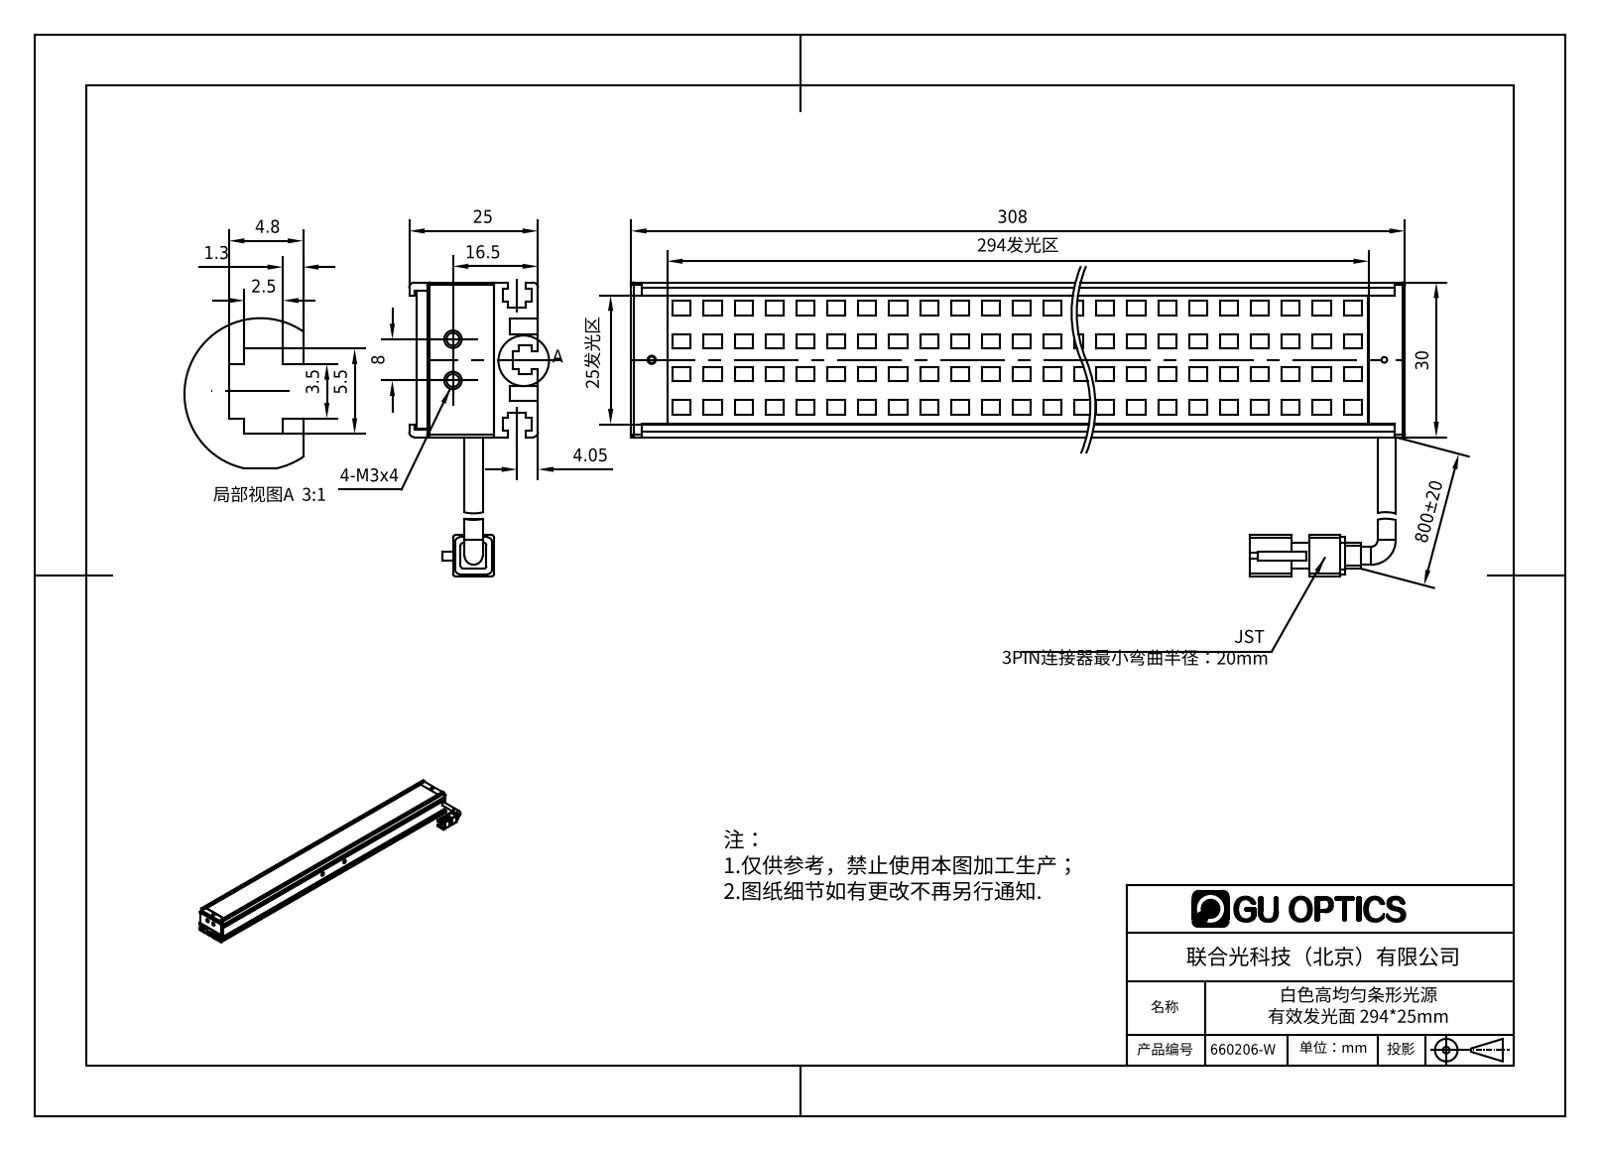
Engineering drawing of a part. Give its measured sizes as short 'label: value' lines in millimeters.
name: 660206-W
written by: SolidWorks 2016 (AUTOMOTIVE_DESIGN)
unit: mm
bodies: 6 solids, 1424 faces (1238 planar, 83 cylindrical, 103 other)
size: 308 × 57 × 25
volume: 104 401 mm³; area: 106 510 mm²
holes: 5× ⌀1.6, 2× ⌀1.5, 2× ⌀1.7, 2× ⌀2.5, 2× ⌀2.8, 2× ⌀3, 1× ⌀1.1, 1× ⌀1.25, 1× ⌀2
bosses: 2× ⌀3.5
rounds: 12× R1, 8× R0.5, 1× R1.65
face distances: 1, 13, 2, 2.5, 3, 27.5, 9.5, 4.5, 12, 15.1
hole spacings: 300, 7, 135, 135.16, 165, 165.13, 300.08, 8
